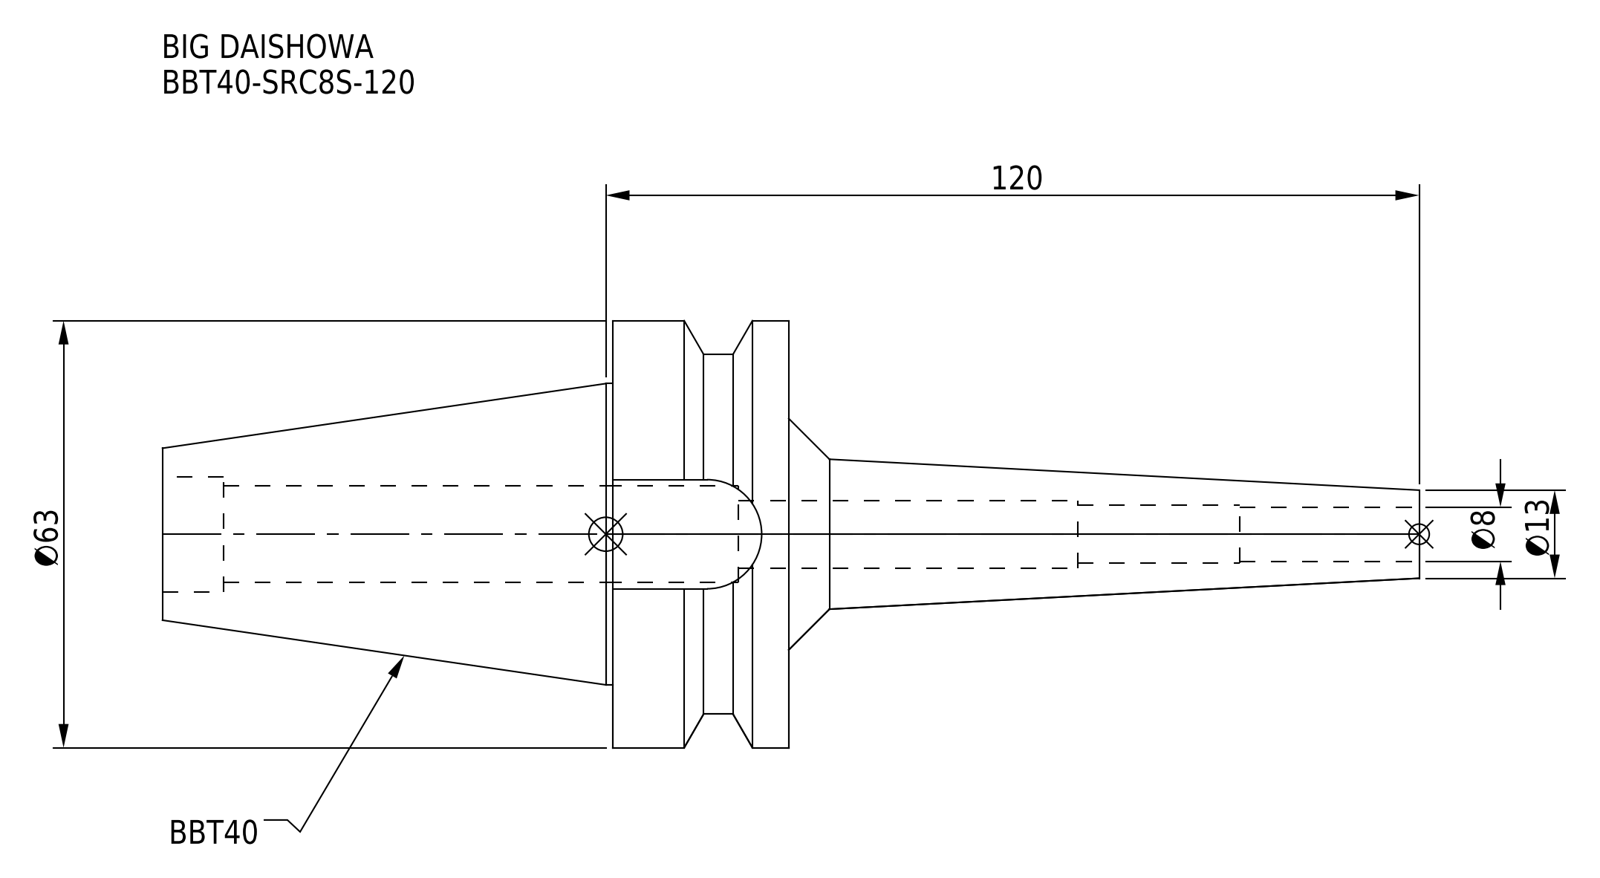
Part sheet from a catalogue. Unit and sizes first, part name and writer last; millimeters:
Units: millimetres
Overall size (bounding box): 185.4 × 63 × 63
Round holes (diameter × count): ⌀8 ×1, ⌀8.5 ×1, ⌀10 ×1, ⌀14.2 ×1, ⌀17 ×1
Round bosses / shafts (diameter × count): ⌀63 ×1, ⌀53 ×1, ⌀44.45 ×1
Partial cylindrical surfaces — rounded edges, fillets, slot ends (radius × count): R8.05 ×1
Main face-to-face distances: 26, 45, 92.4, 66.4, 16.1, 93, 119, 185.4, 100.4, 7.4
Volume: 140 210 mm³ · Surface area: 30 231 mm²
Bodies: 1 solid, 46 faces (14 planar, 22 cylindrical, 10 other)
Part name (STEP PRODUCT): BBT40-SRC8S-120
STEP written by: CREO PARAMETRIC BY PTC INC, 2016380 (AUTOMOTIVE_DESIGN)
